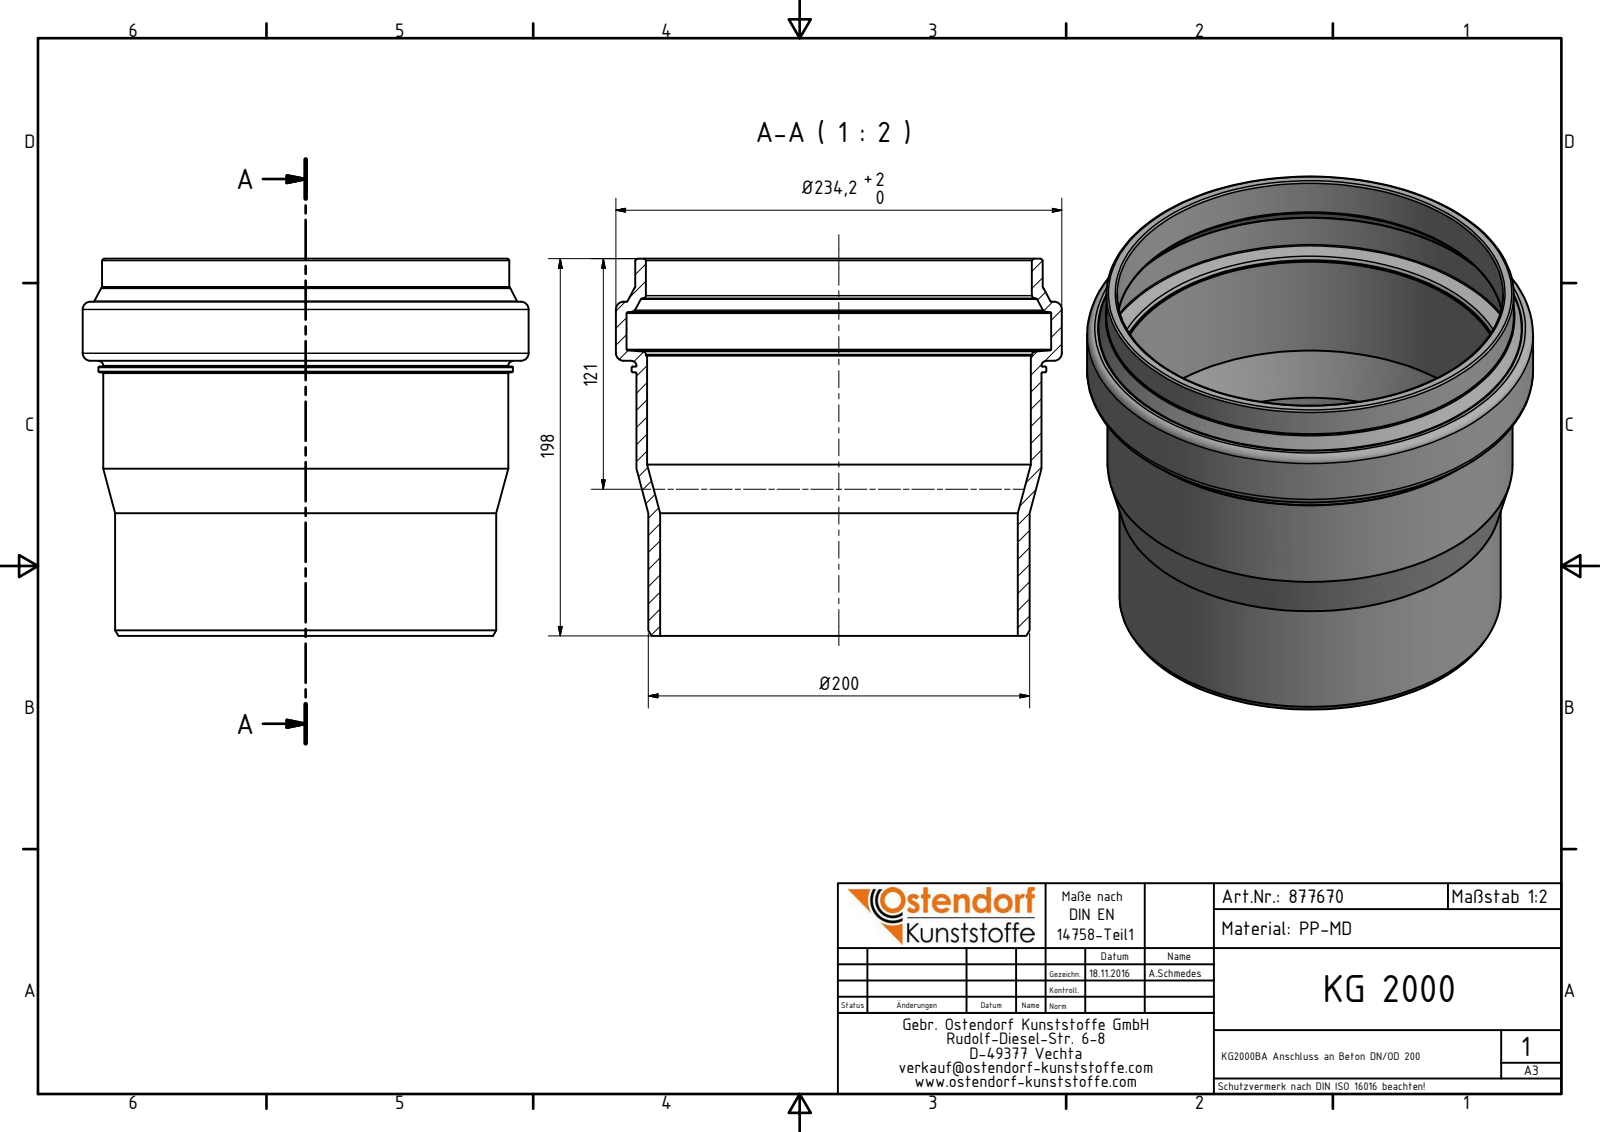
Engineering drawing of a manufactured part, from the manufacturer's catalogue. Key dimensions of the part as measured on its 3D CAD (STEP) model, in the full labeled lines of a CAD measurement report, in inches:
Part name (STEP PRODUCT): 877670 KG2000BA Anschluss an Beton DN_OD 200
STEP written by: Autodesk Inventor 2016 (AUTOMOTIVE_DESIGN)
Units: inches
Bodies: 1 solid, 43 faces (7 planar, 10 cylindrical, 26 other)
Overall size (bounding box): 9.22 × 9.22 × 7.795
Volume: 49.47 in³ · Surface area: 441.3 in²
Round holes (diameter × count): ⌀7.394 ×1, ⌀7.933 ×1, ⌀7.98 ×1, ⌀8.78 ×1
Round bosses / shafts (diameter × count): ⌀9.22 ×1, ⌀8.571 ×1, ⌀8.421 ×1, ⌀8.374 ×1, ⌀7.882 ×1
Main face-to-face distances: 5.685, 7.795, 2.11, 0.118, 6.906, 1.22, 0.89, 5.567, 1.339, 2.228
